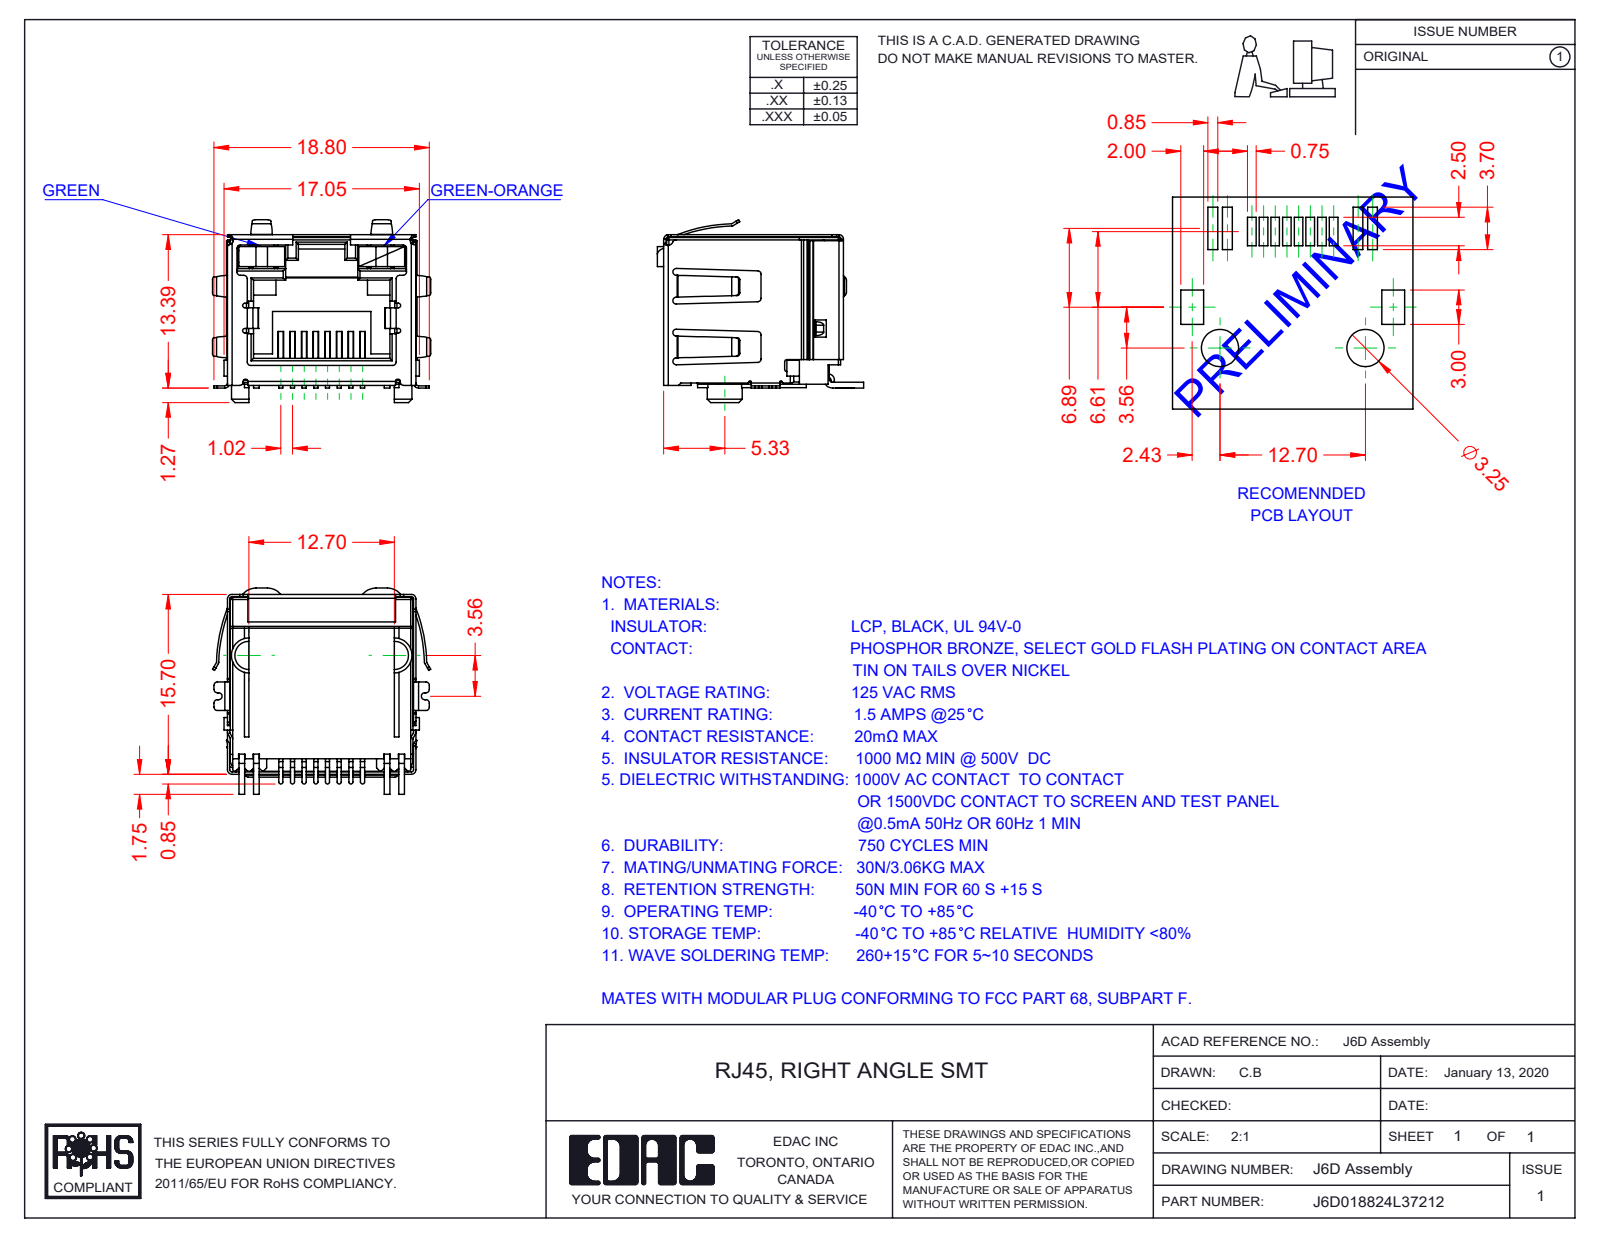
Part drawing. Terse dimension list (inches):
name: 6D LED LH_3-Green; 6D Insulator; J6D018824L37212; 6D Contacts (+2 more)
written by: SolidWorks 2016 (CONFIG_CONTROL_DESIGN)
unit: in
bodies: 12 solids, 1031 faces (702 planar, 284 cylindrical, 45 other)
size: 0.75 × 0.709 × 0.628
volume: 0.109 in³; area: 7.434 in²
rounds: 55× R0.012, 40× R0.008, 19× R0.016, 16× R0.01, 12× R0.004, 8× R0.006, 8× R0.007, 6× R0.02
face distances: 0.63, 0.638, 0.64, 0.089, 0.039, 0.628, 0.504, 0.018, 0.514, 0.417
